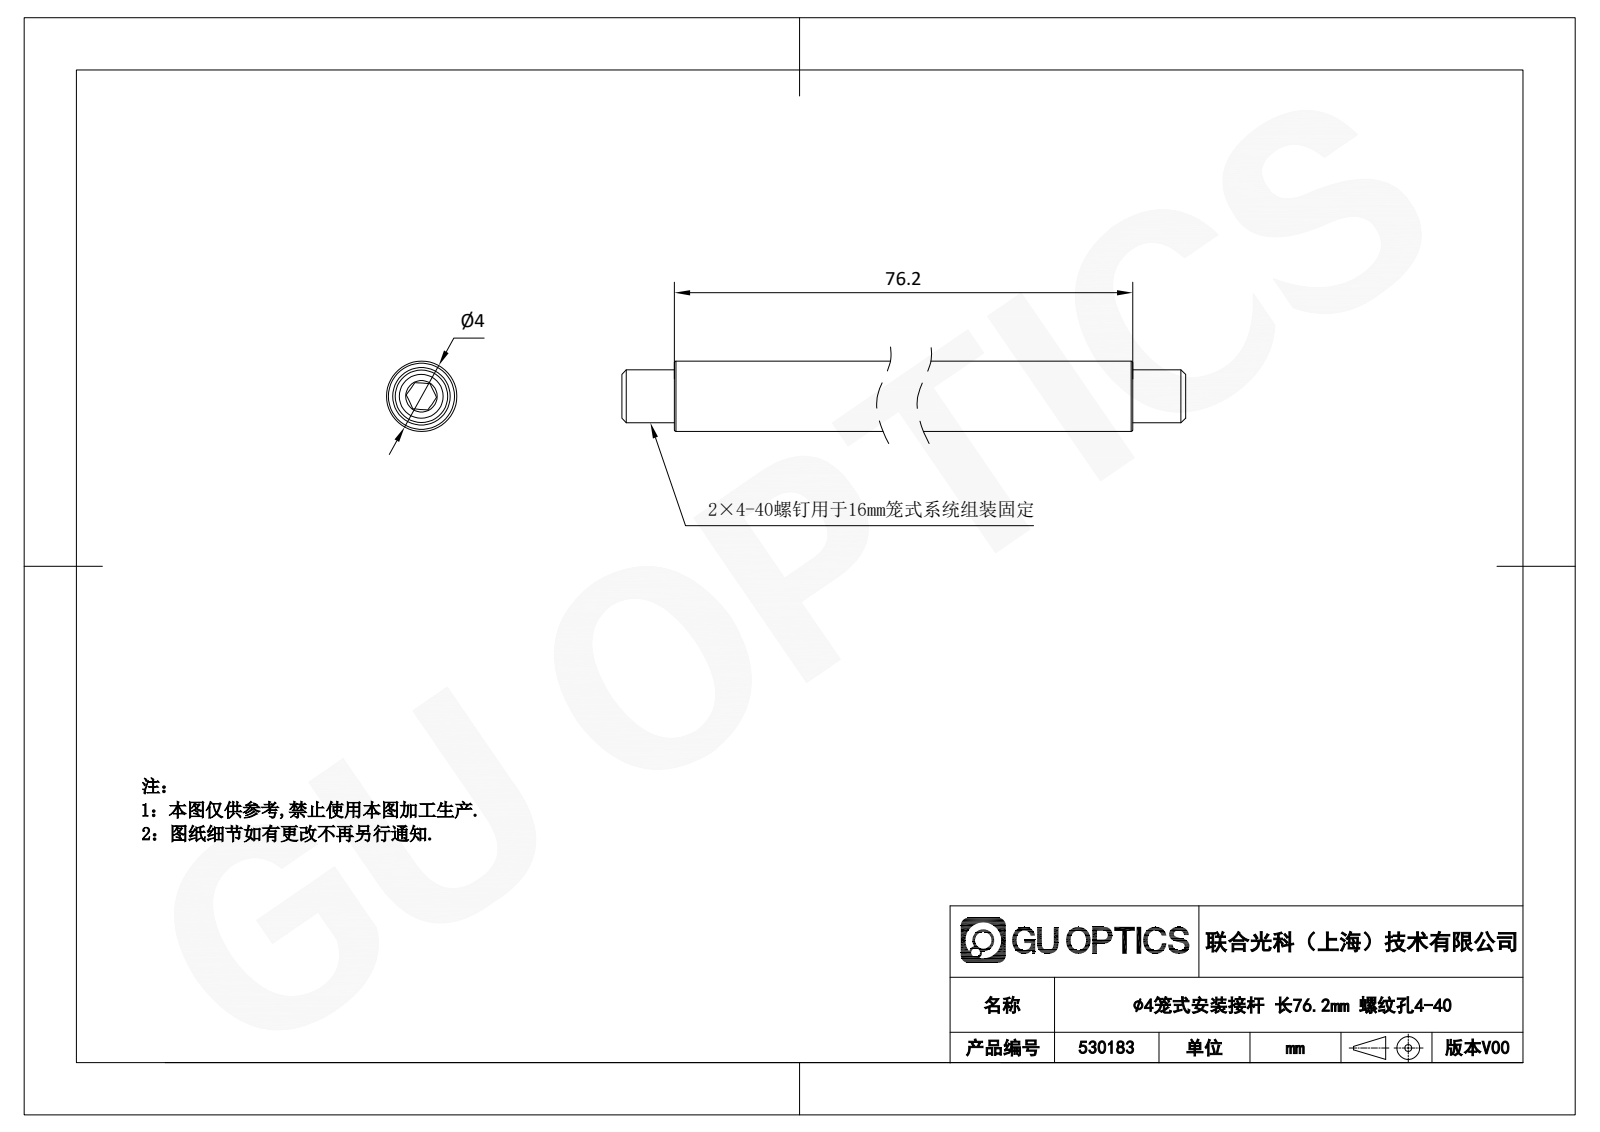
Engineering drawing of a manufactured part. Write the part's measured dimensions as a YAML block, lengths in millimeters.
part_name: "530183"
step_written_by: "SolidWorks 2020 (CONFIG_CONTROL_DESIGN)"
units: millimeters
bodies: {solids: 3, faces: 37, planar: 20, cylindrical: 5, other: 12}
overall_size: [86.2, 4, 4]
volume: 1007
surface_area: 1247
round_holes:
  - {diameter: 2.5, count: 1}
round_bosses_or_shafts:
  - {diameter: 4, count: 1}
  - {diameter: 3, count: 1}
face_to_face_distances: [3, 73.2, 5, 8, 78.2, 81.2, 1.5, 76.2, 1, 85.2]
